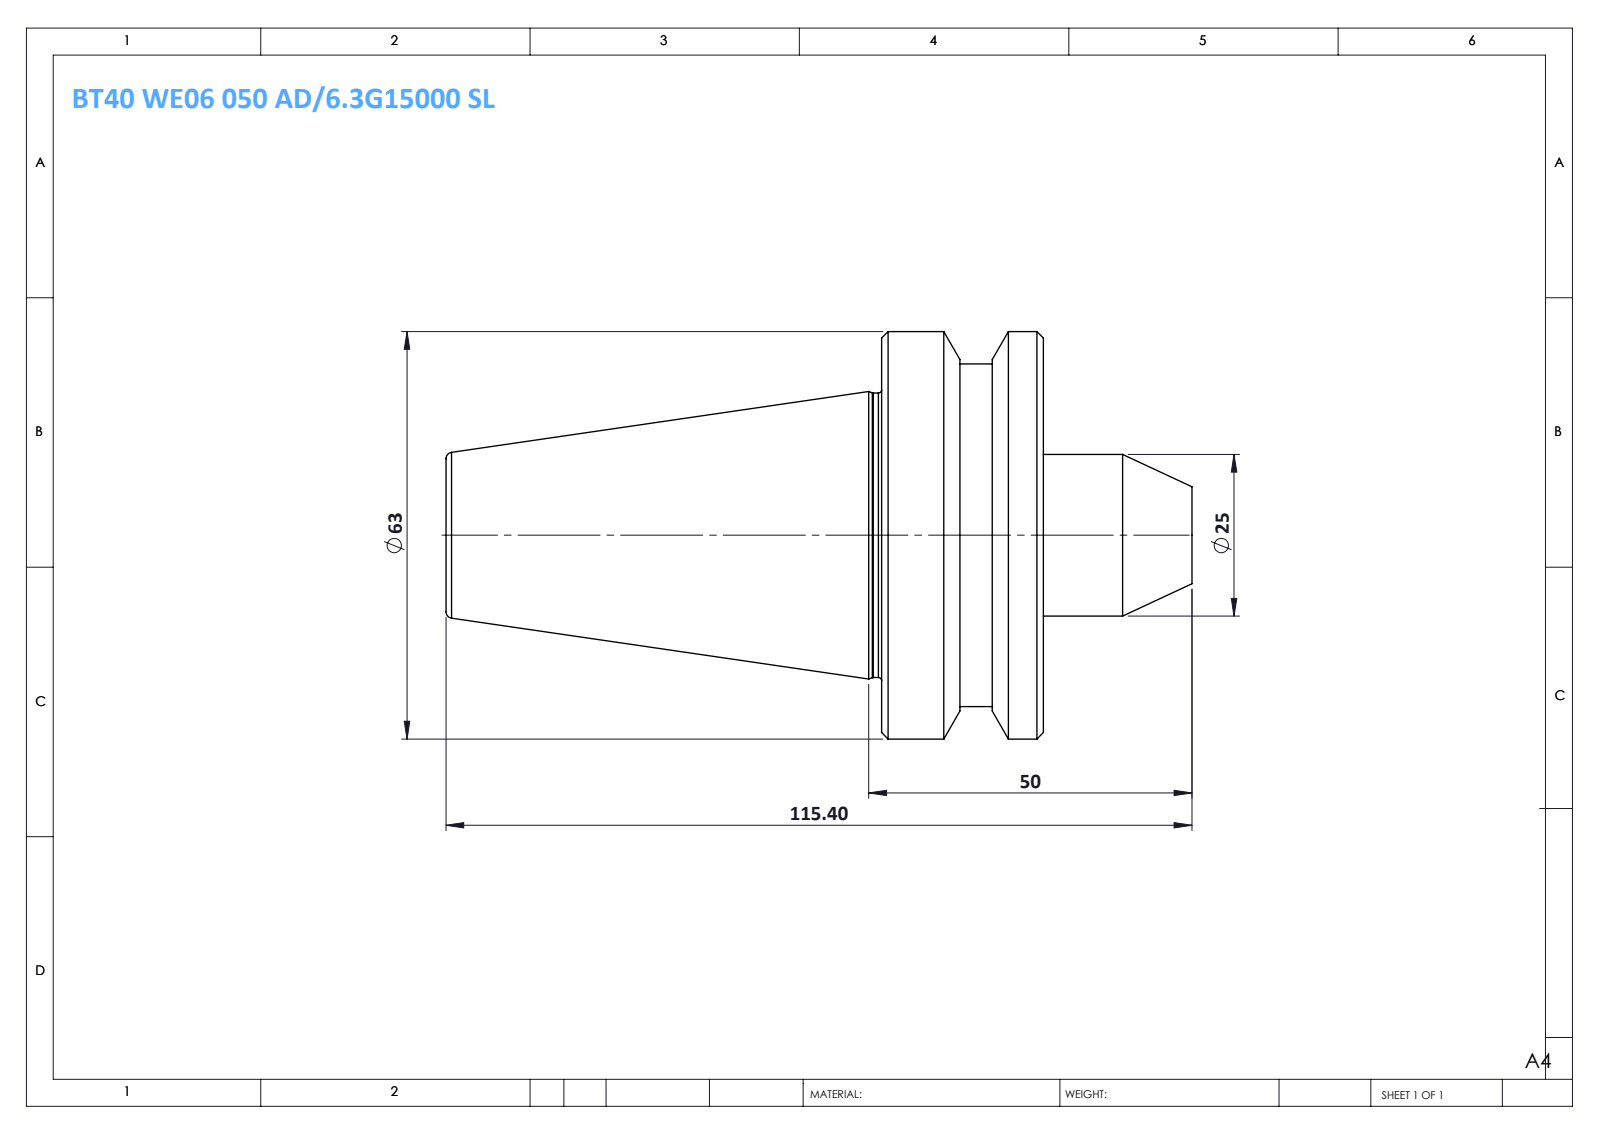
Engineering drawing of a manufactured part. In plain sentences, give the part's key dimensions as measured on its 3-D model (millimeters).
The part is named "BT40 WE06 050 AD-6.3G15000 SL". Its 3-D file was written by "SolidWorks 2014 (CONFIG_CONTROL_DESIGN)". It is 1 solid with 36 faces: 6 planar, 10 cylindrical and 20 other. Overall it measures 115.4 by 63 by 63 millimeters. Its volume is 147 812 cubic millimeters and its surface area 19 726 square millimeters. Round bosses or shafts: 1 of diameter 63, 1 of diameter 53, 1 of diameter 44, 1 of diameter 25. The main face-to-face distances are 25, 92.4, 67.4, 23, 48, 115.4, 35.9, 12.9, 12.1, 79.5.
